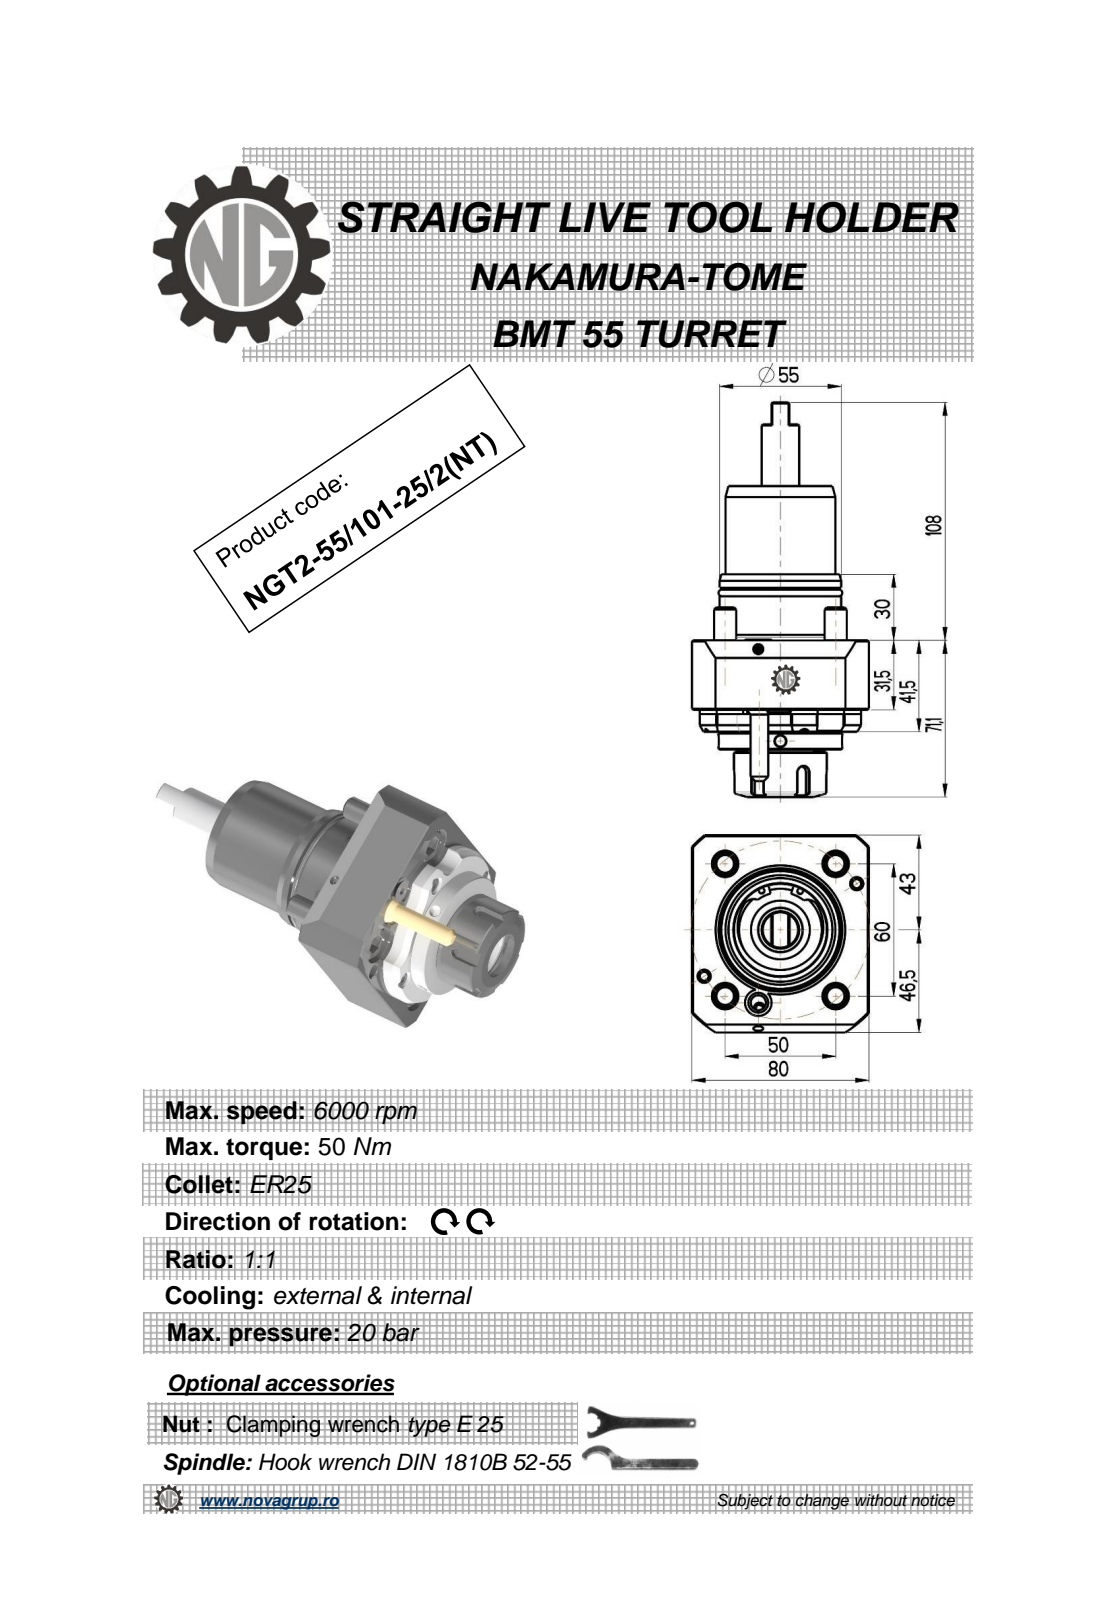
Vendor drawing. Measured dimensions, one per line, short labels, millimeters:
name: NGT2_55_101_25_1_NT
written by: PRO/ENGINEER BY PARAMETRIC TECHNOLOGY CORPORATION, 2010280 (CONFIG_CONTROL_DESIGN)
unit: mm
bodies: 2 solids, 283 faces (91 planar, 78 cylindrical, 114 other)
size: 179.1 × 89.5 × 80
volume: 463 976 mm³; area: 53 081 mm²
holes: 3× ⌀5, 1× ⌀3, 1× ⌀6.8, 1× ⌀20.3
bosses: 4× ⌀10, 1× ⌀56, 1× ⌀55, 1× ⌀54.4, 1× ⌀50, 1× ⌀49.7, 1× ⌀43, 1× ⌀42
rounds: 6× R0.22, 5× R3, 4× R8.5, 2× R0.8, 2× R6, 1× R20.44, 1× R30.55, 1× R36.5
face distances: 31.5, 80, 10, 41.5, 8, 49.5, 18, 70, 101.5, 111.5
hole spacings: 2.55, 34.48, 36.75
